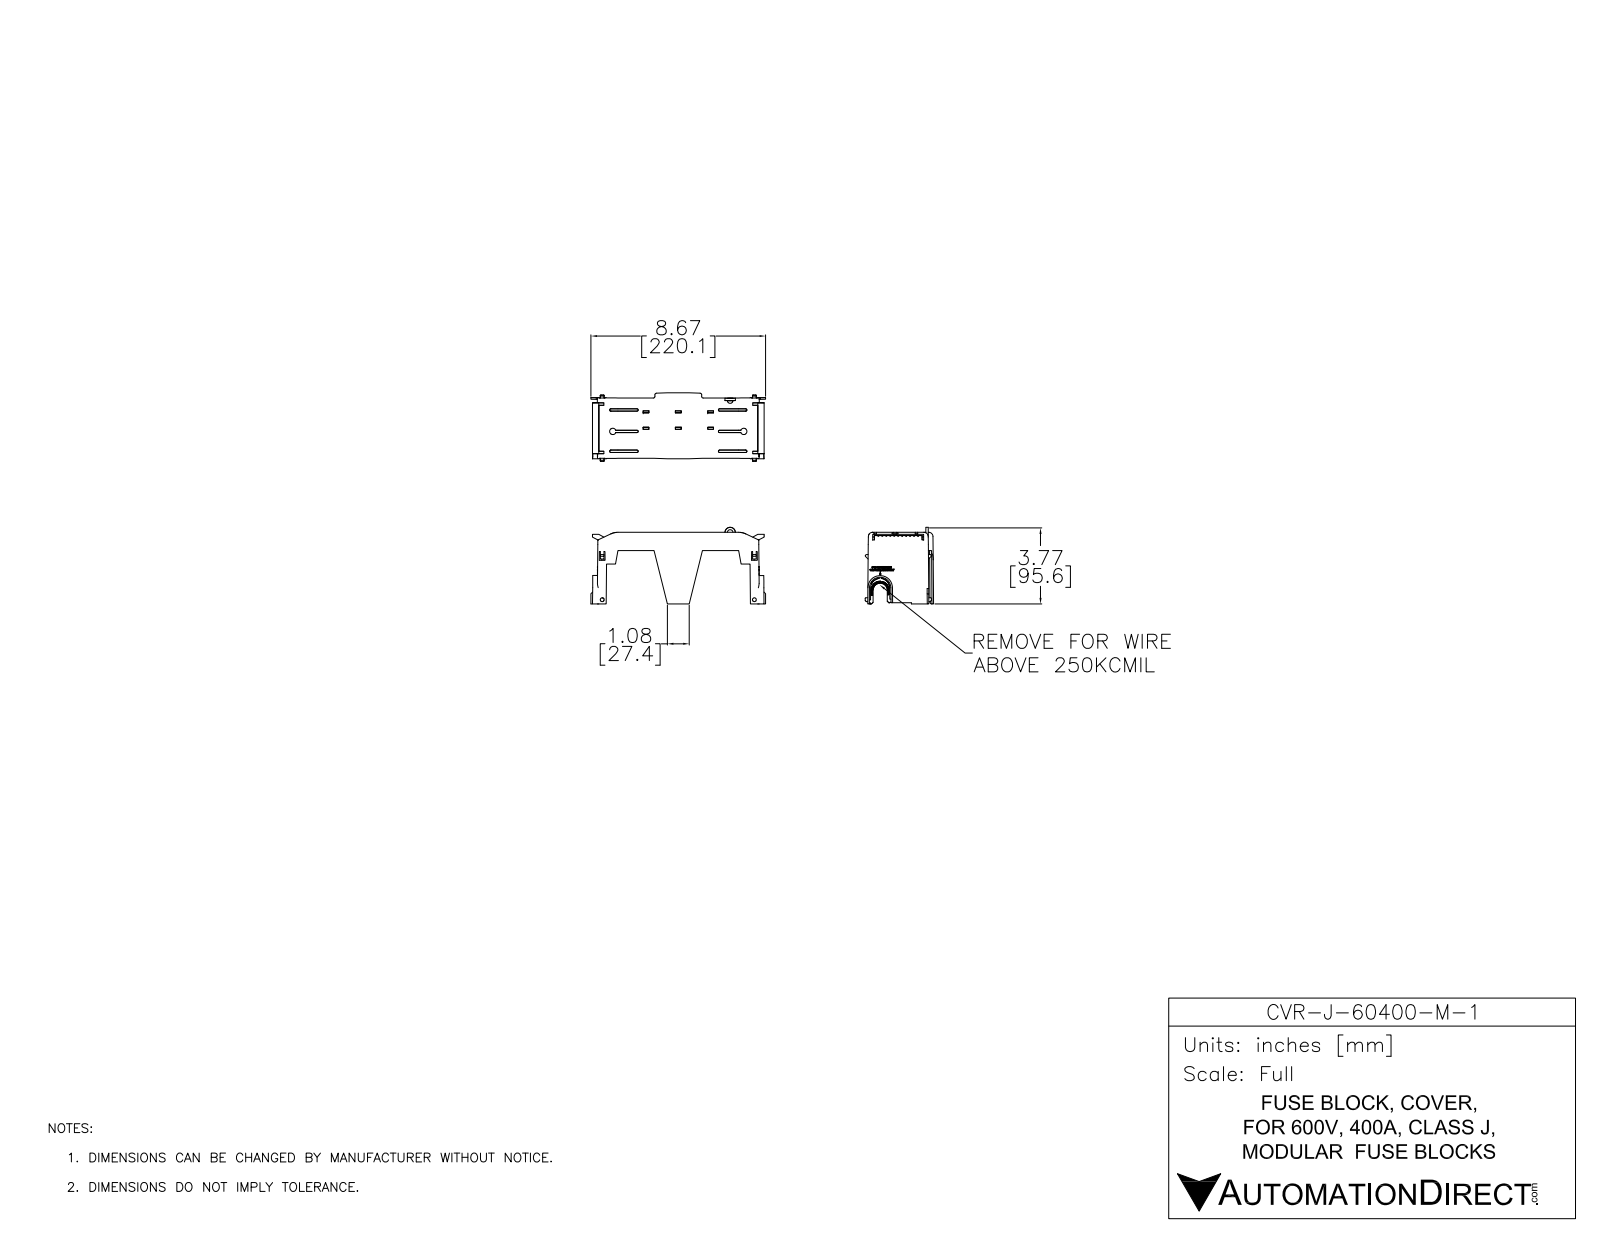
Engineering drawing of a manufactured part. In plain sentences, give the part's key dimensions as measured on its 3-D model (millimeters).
The part is named "CVR-J-60400-M-1". Its 3-D file was written by "SolidWorks 2017 (AUTOMOTIVE_DESIGN)". It is 1 solid with 2395 faces: 1608 planar, 122 cylindrical and 665 other. Overall it measures 220.1 by 96.6 by 86.3 millimeters. Its volume is 104 800 cubic millimeters and its surface area 110 400 square millimeters. Round holes: 1 of diameter 7. Partial cylindrical surfaces (rounded edges, fillets, slot ends): 18 of radius 1, 11 of radius 3, 8 of radius 3.5, 7 of radius 5.5, 4 of radius 2, 2 of radius 0.3, 2 of radius 0.5, 2 of radius 1. The main face-to-face distances are 2, 6, 8, 4, 20.4, 3, 5, 17, 37.4, 88.3.
